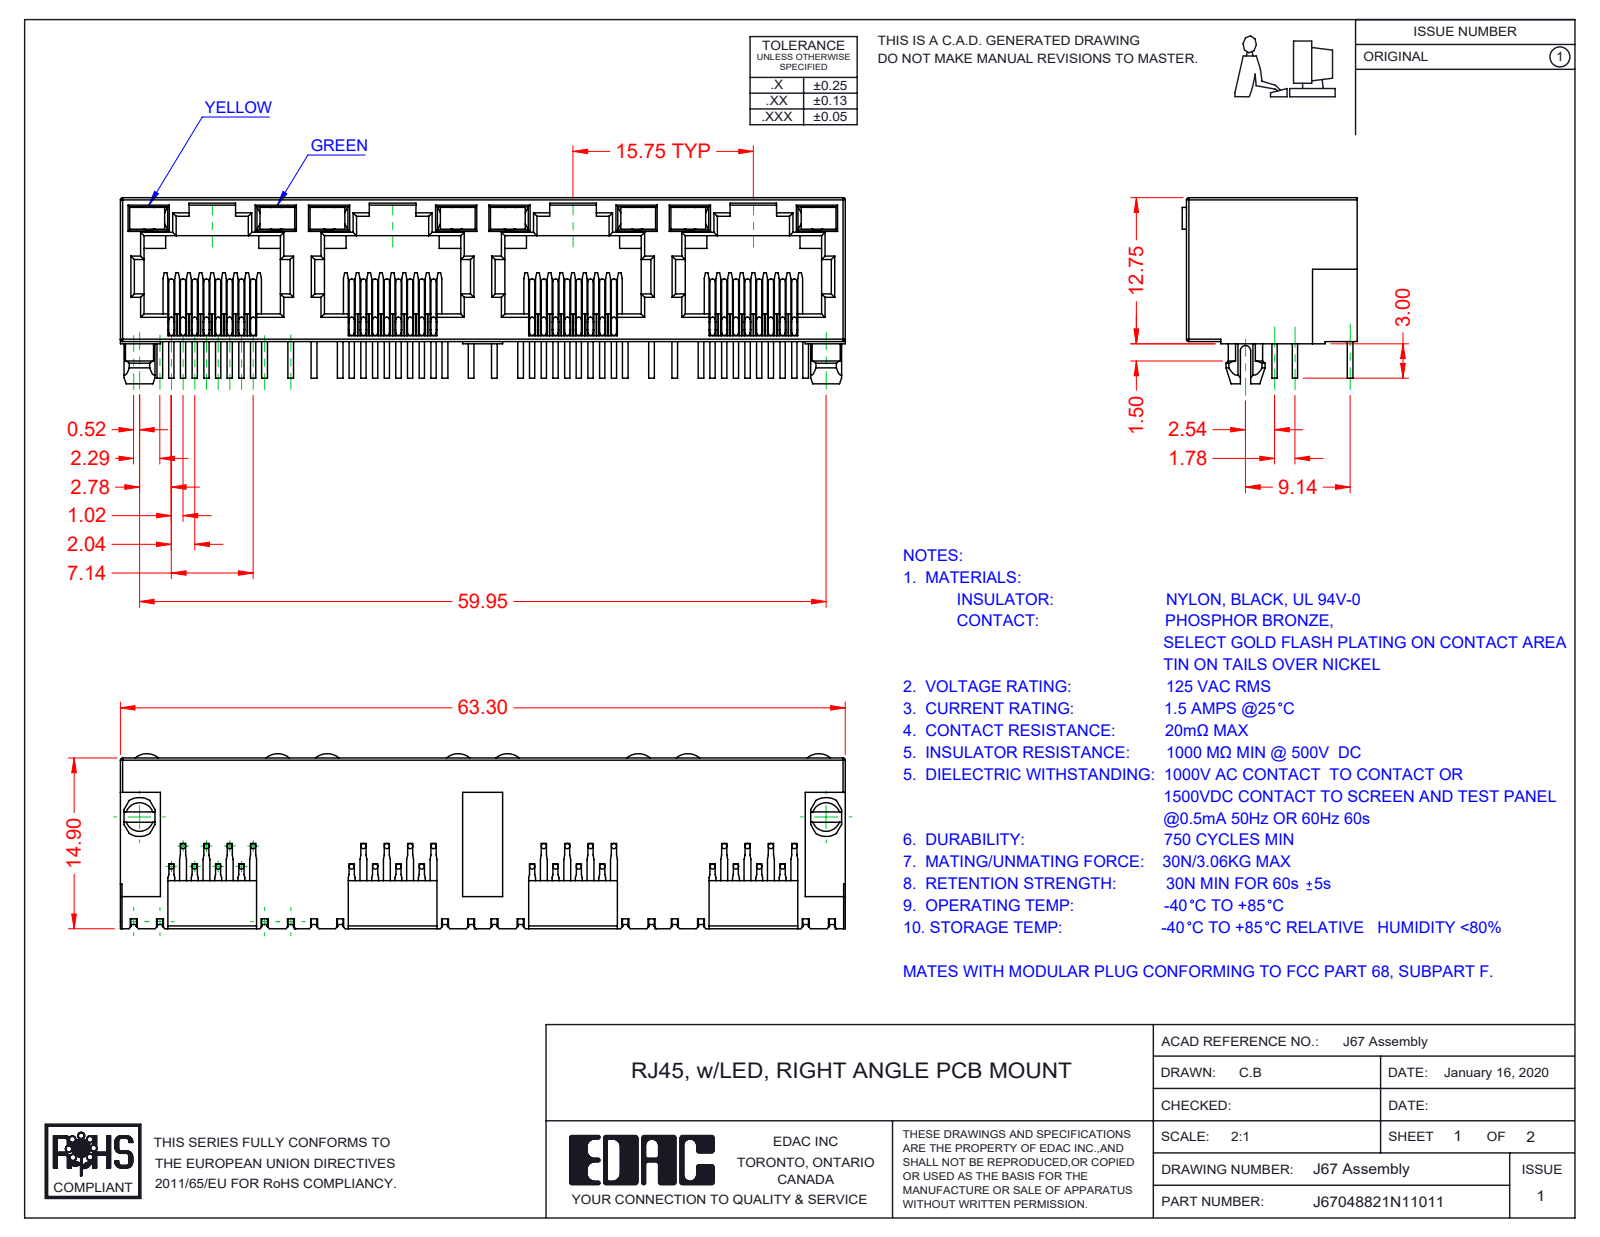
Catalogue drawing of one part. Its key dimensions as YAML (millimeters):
part_name: "J67048822N13011; 67 LED LH_1-Yellow; 67 Insulator; 67 Contacts (+1 more)"
step_written_by: "SolidWorks 2016 (CONFIG_CONTROL_DESIGN)"
units: millimeters
bodies: {solids: 41, faces: 2465, planar: 1781, cylindrical: 476, other: 208}
overall_size: [63.3, 16.25, 15.28]
volume: 5159
surface_area: 11573
round_bosses_or_shafts:
  - {diameter: 0.46, count: 96}
partial_cylinders:
  - {radius: 0.2, count: 66}
  - {radius: 0.3, count: 29}
  - {radius: 0.45, count: 9}
  - {radius: 1.55, count: 8}
  - {radius: 1.5, count: 2}
  - {radius: 1.7, count: 2}
  - {radius: 0.35, count: 1}
  - {radius: 1, count: 1}
face_to_face_distances: [0.5, 12.55, 1.89, 0.89, 10, 15.75, 1, 1.39, 11, 11.89]
